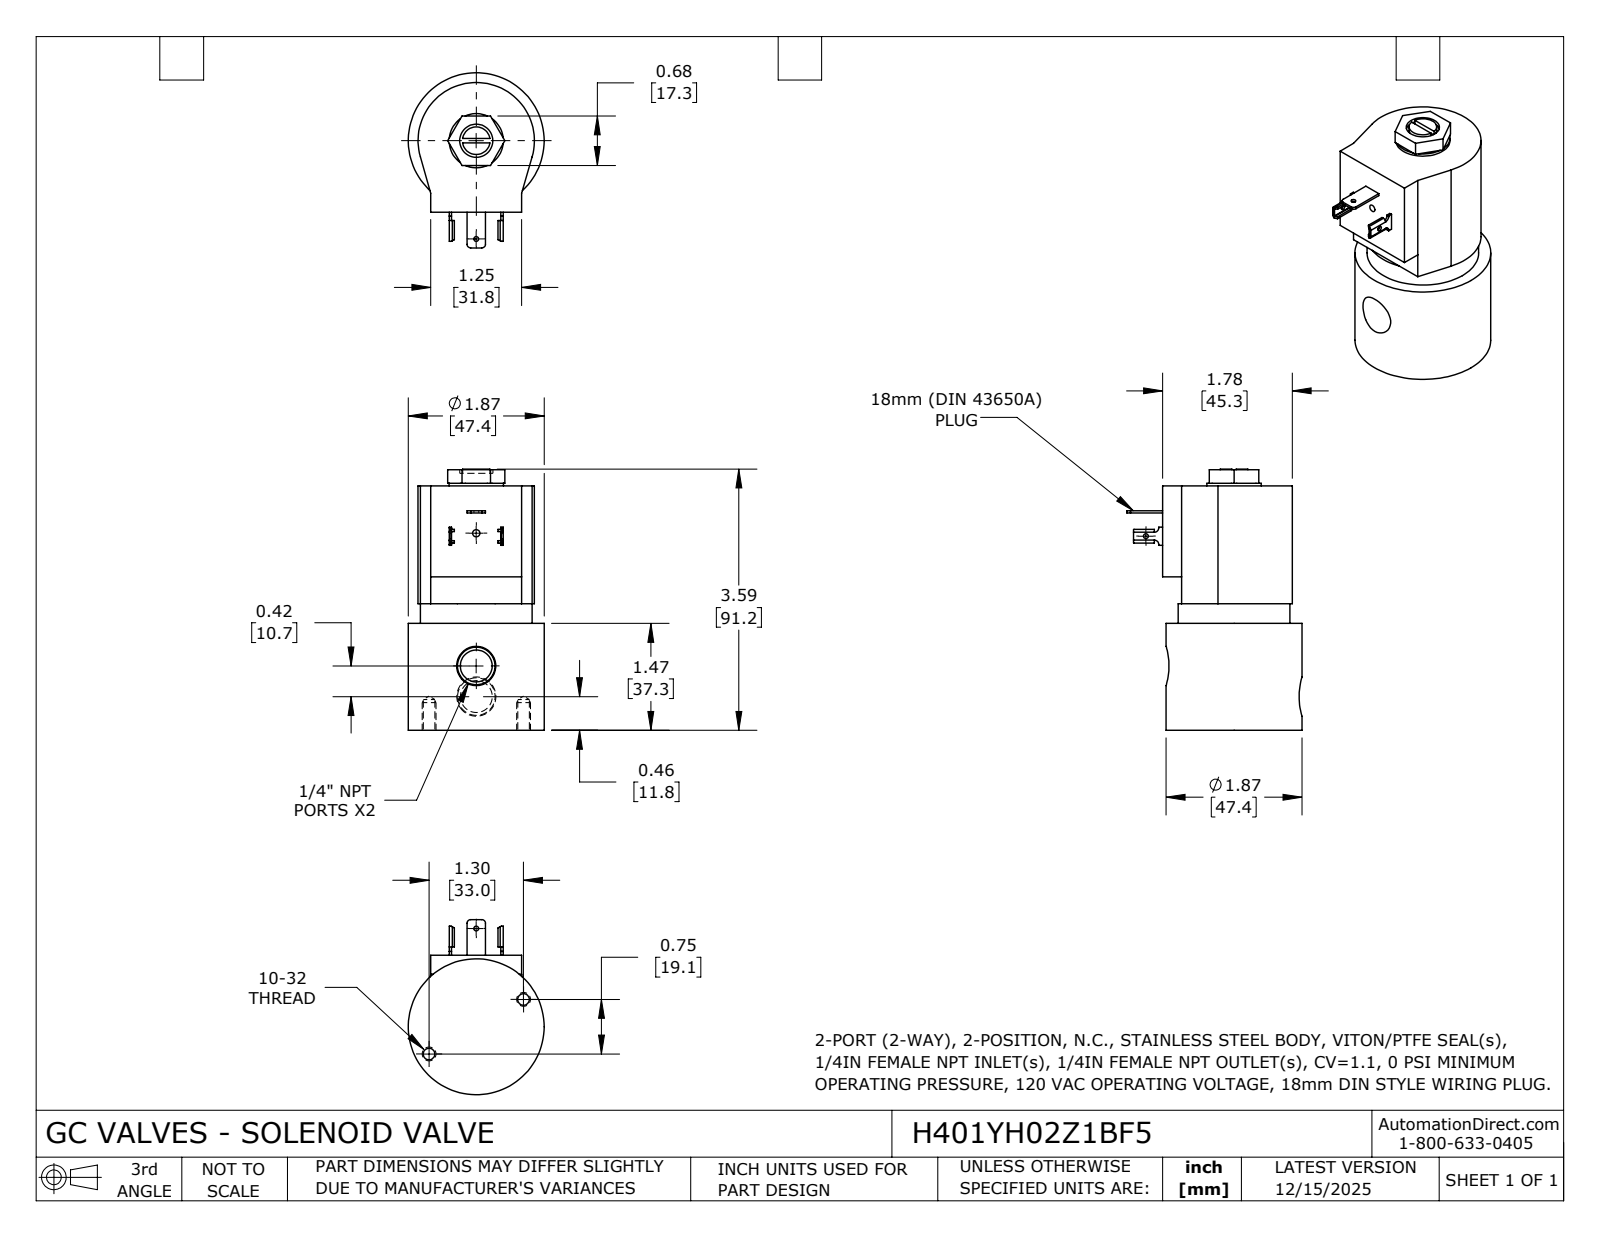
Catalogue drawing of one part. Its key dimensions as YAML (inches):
part_name: "H401YH02Z1BF5"
step_written_by: "SolidWorks 2024 (CONFIG_CONTROL_DESIGN)"
units: inches
bodies: {solids: 1, faces: 132, planar: 75, cylindrical: 43, other: 14}
overall_size: [3.591, 2.407, 1.868]
volume: 8.118
surface_area: 29.18
round_holes:
  - {diameter: 0.159, count: 2}
  - {diameter: 0.438, count: 2}
  - {diameter: 0.066, count: 1}
  - {diameter: 0.067, count: 1}
  - {diameter: 0.1, count: 1}
  - {diameter: 0.456, count: 1}
round_bosses_or_shafts:
  - {diameter: 1.868, count: 1}
  - {diameter: 1.535, count: 1}
  - {diameter: 0.746, count: 1}
  - {diameter: 0.38, count: 1}
partial_cylinders:
  - {radius: 0.006, count: 4}
  - {radius: 0.041, count: 4}
  - {radius: 0.05, count: 2}
  - {radius: 0.06, count: 2}
  - {radius: 0.8, count: 1}
face_to_face_distances: [3.36, 1.47, 1.89, 0.26, 2.11, 0.64, 1.25, 1.25, 3.583, 2.113]
hole_center_spacings: [0.75, 0.422, 1.171, 1.35, 1.5, 1.824, 1.843, 2.246]
